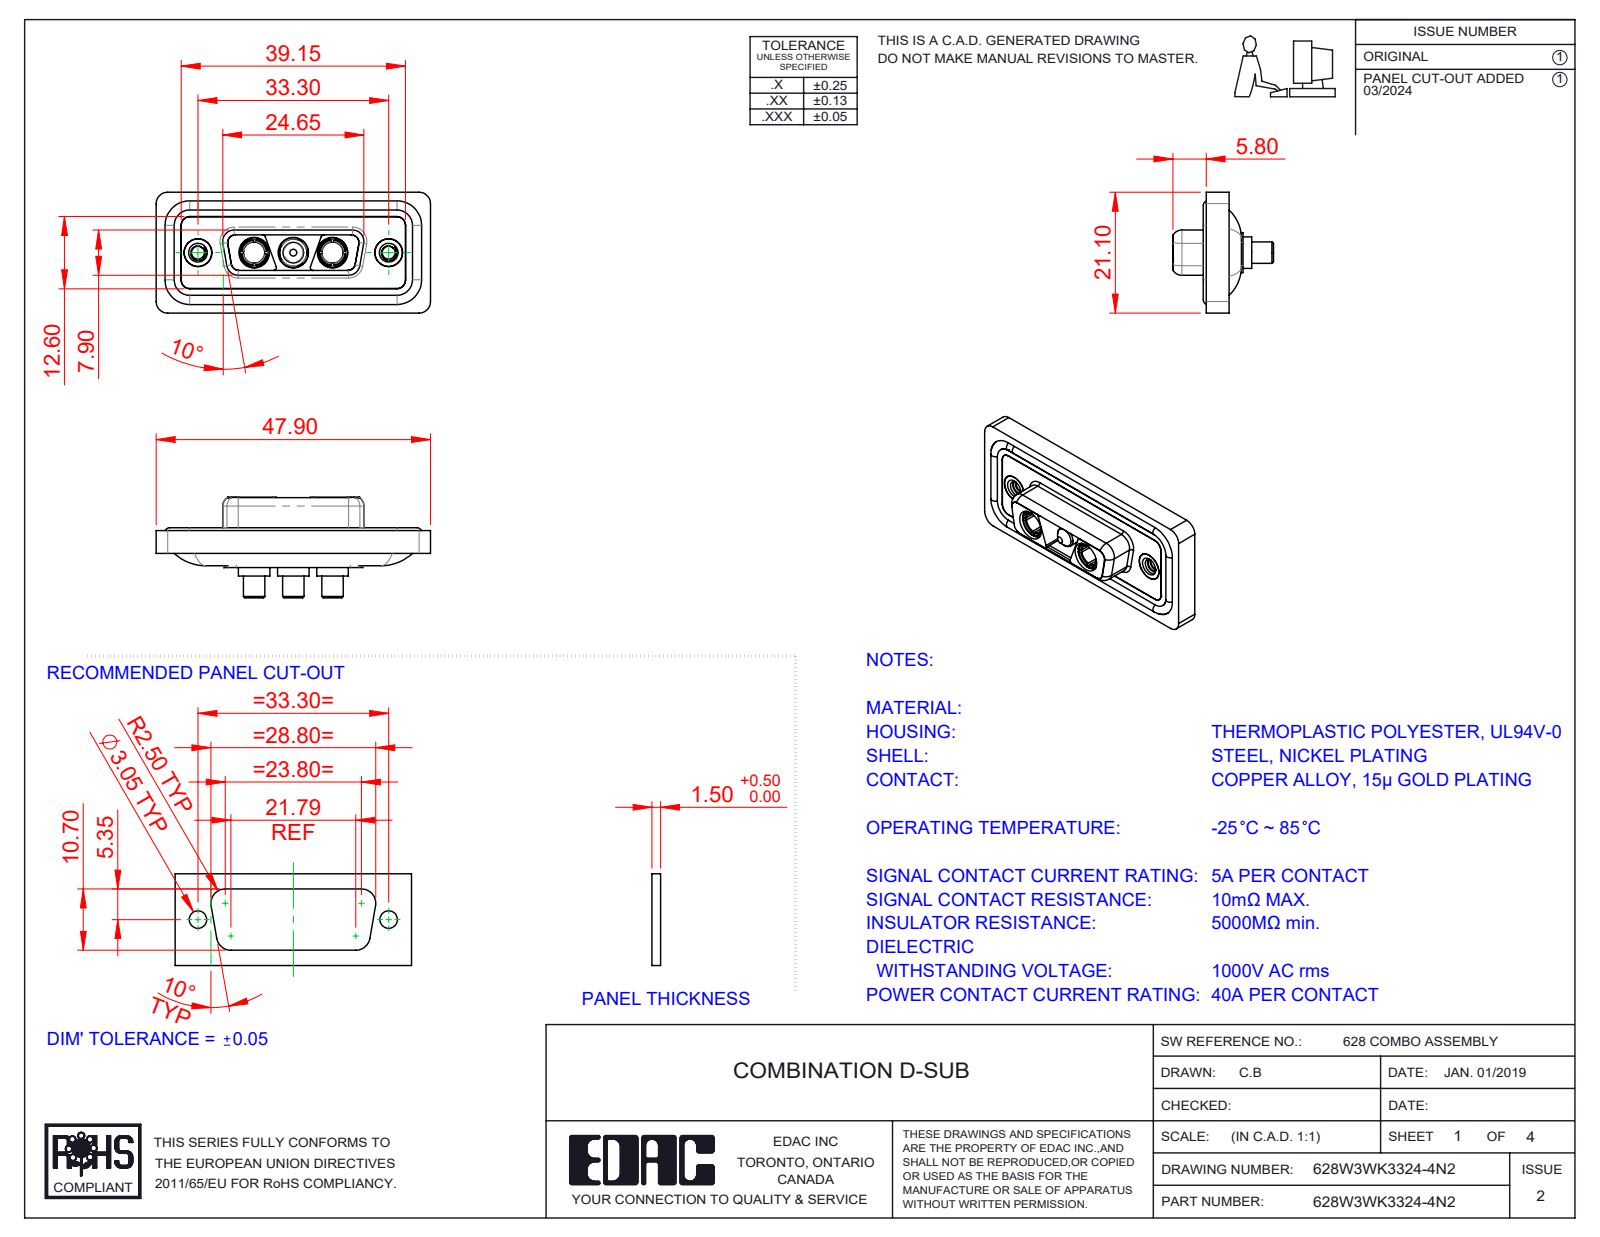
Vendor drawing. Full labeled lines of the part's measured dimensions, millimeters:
Part name (STEP PRODUCT): 628Combo Waterproof Housing_15 Contacts; 628Combo Shell Rear_15 Contacts; Power Socket_40A S; 628W3WK3324-4N2 (+4 more)
STEP written by: SolidWorks 2023 (CONFIG_CONTROL_DESIGN)
Units: millimetres
Bodies: 13 solids, 583 faces (178 planar, 258 cylindrical, 147 other)
Overall size (bounding box): 47.9 × 21.1 × 17.55
Volume: 5 933 mm³ · Surface area: 9 537 mm²
Round holes (diameter × count): ⌀4.85 ×5, ⌀5.3 ×3, ⌀2.26 ×2, ⌀3.7 ×2, ⌀4 ×2, ⌀4.05 ×2, ⌀5 ×2
Round bosses / shafts (diameter × count): ⌀1.6 ×4, ⌀5.5 ×3, ⌀5.2 ×3, ⌀4.75 ×3, ⌀3.75 ×3, ⌀4.96 ×2, ⌀4.95 ×2, ⌀4.8 ×2
Partial cylindrical surfaces — rounded edges, fillets, slot ends (radius × count): R1.5 ×22, R2 ×20, R1.35 ×12, R0.5 ×8, R1.6 ×8, R0.25 ×4, R0.6 ×4, R0.65 ×4
Main face-to-face distances: 0.4, 1.6, 0.5, 1.8, 1.1, 2.9, 5.65, 7.05, 5.35, 1.5
Hole centre spacings: 6.85, 9.8, 16.65, 23.5, 13.7, 33.3
